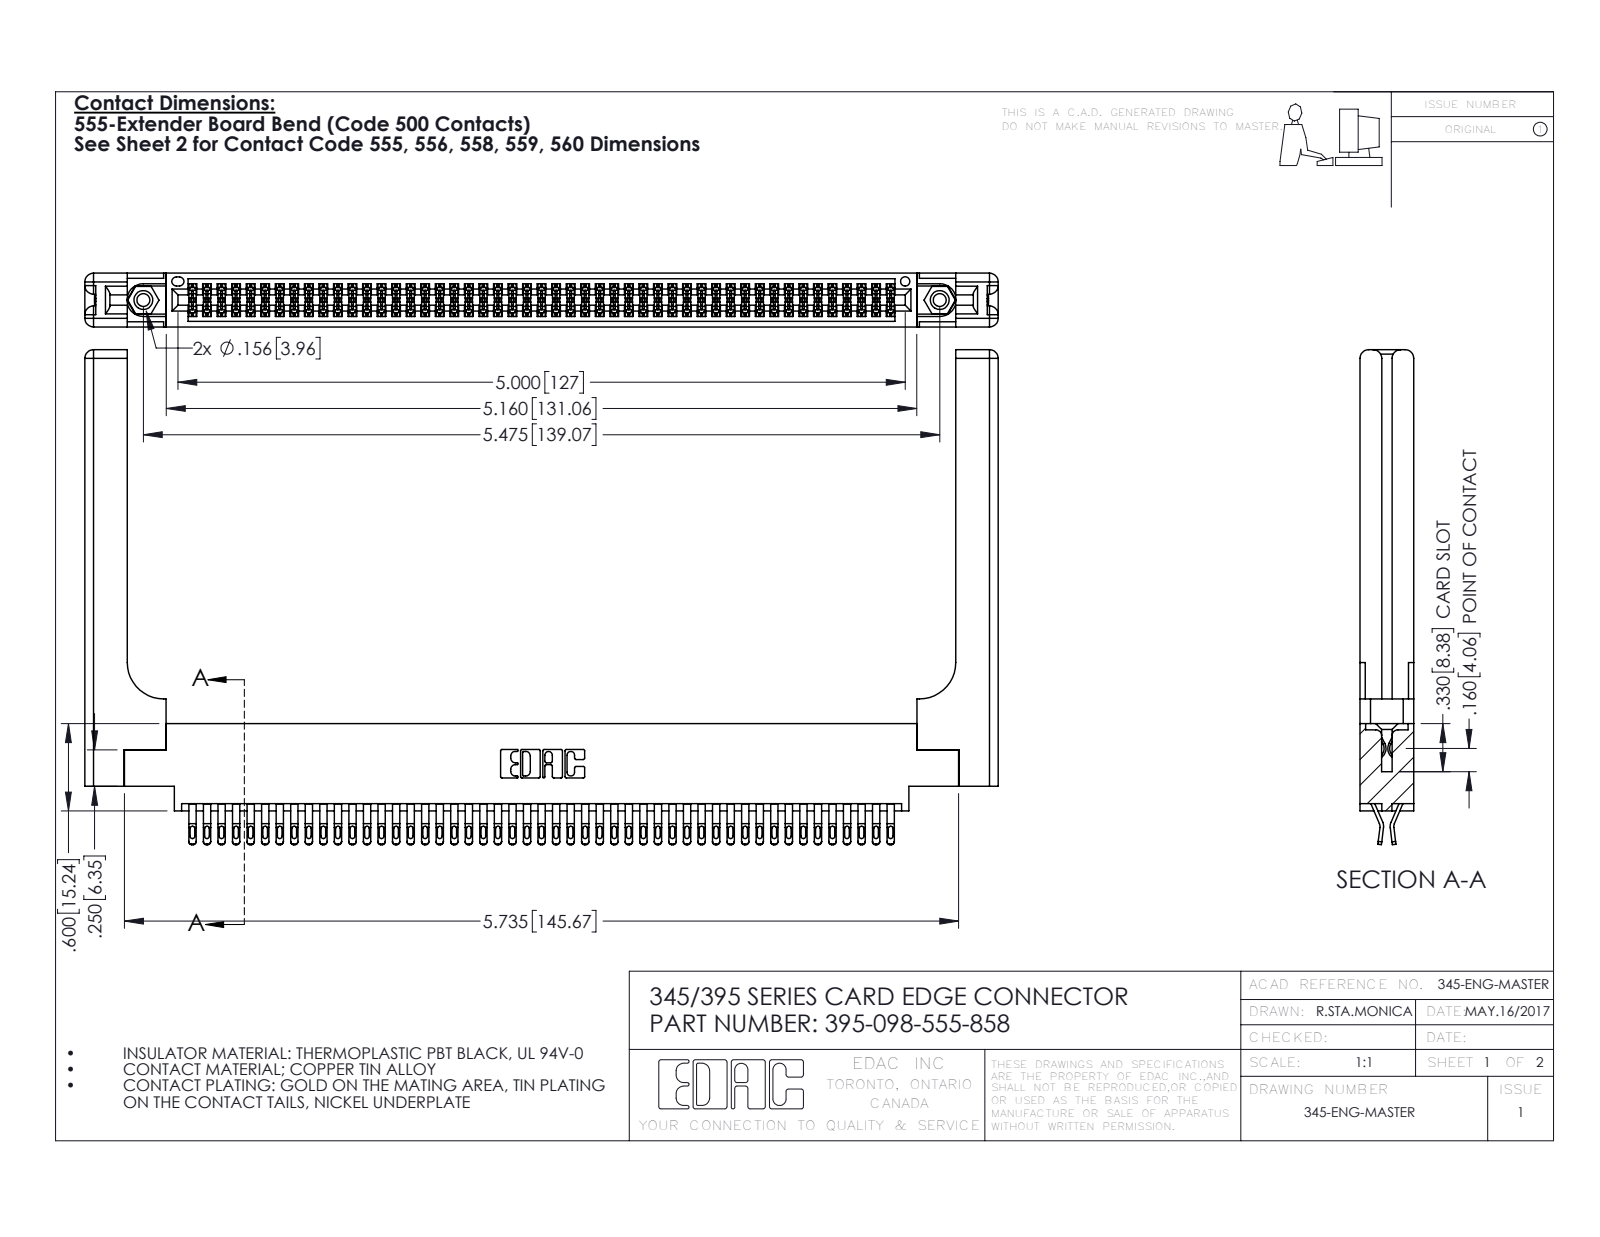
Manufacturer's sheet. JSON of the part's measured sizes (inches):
{"part_name": "395-098-555-858; 345-250-001_345-250-001-102; 345-220-058_345-220-058; 345 Part_0.170 Offset - 0.156 Dia-TH (+1 more)", "step_written_by": "SolidWorks 2016 (CONFIG_CONTROL_DESIGN)", "units": "inches", "bodies": {"solids": 103, "faces": 5874, "planar": 3270, "cylindrical": 2544, "other": 60}, "overall_size": [6.279, 3.402, 0.37], "volume_in3": 1.477, "surface_area_in2": 45.84, "round_holes": [[0.089, 2], [0.125, 2], [0.156, 2], [0.064, 1]], "round_bosses_or_shafts": [[0.155, 2]], "partial_cylinders_radius": [[0.016, 245], [0.02, 196], [0.006, 147], [0.01, 22], [0.06, 16], [0.007, 6], [0.031, 6], [0.026, 3]], "face_to_face_distances": [0.072, 0.37, 0.298, 0.025, 0.098, 0.272, 0.2, 0.225, 0.148, 0.15], "hole_center_spacings": [0.27, 5.239, 5.475]}
